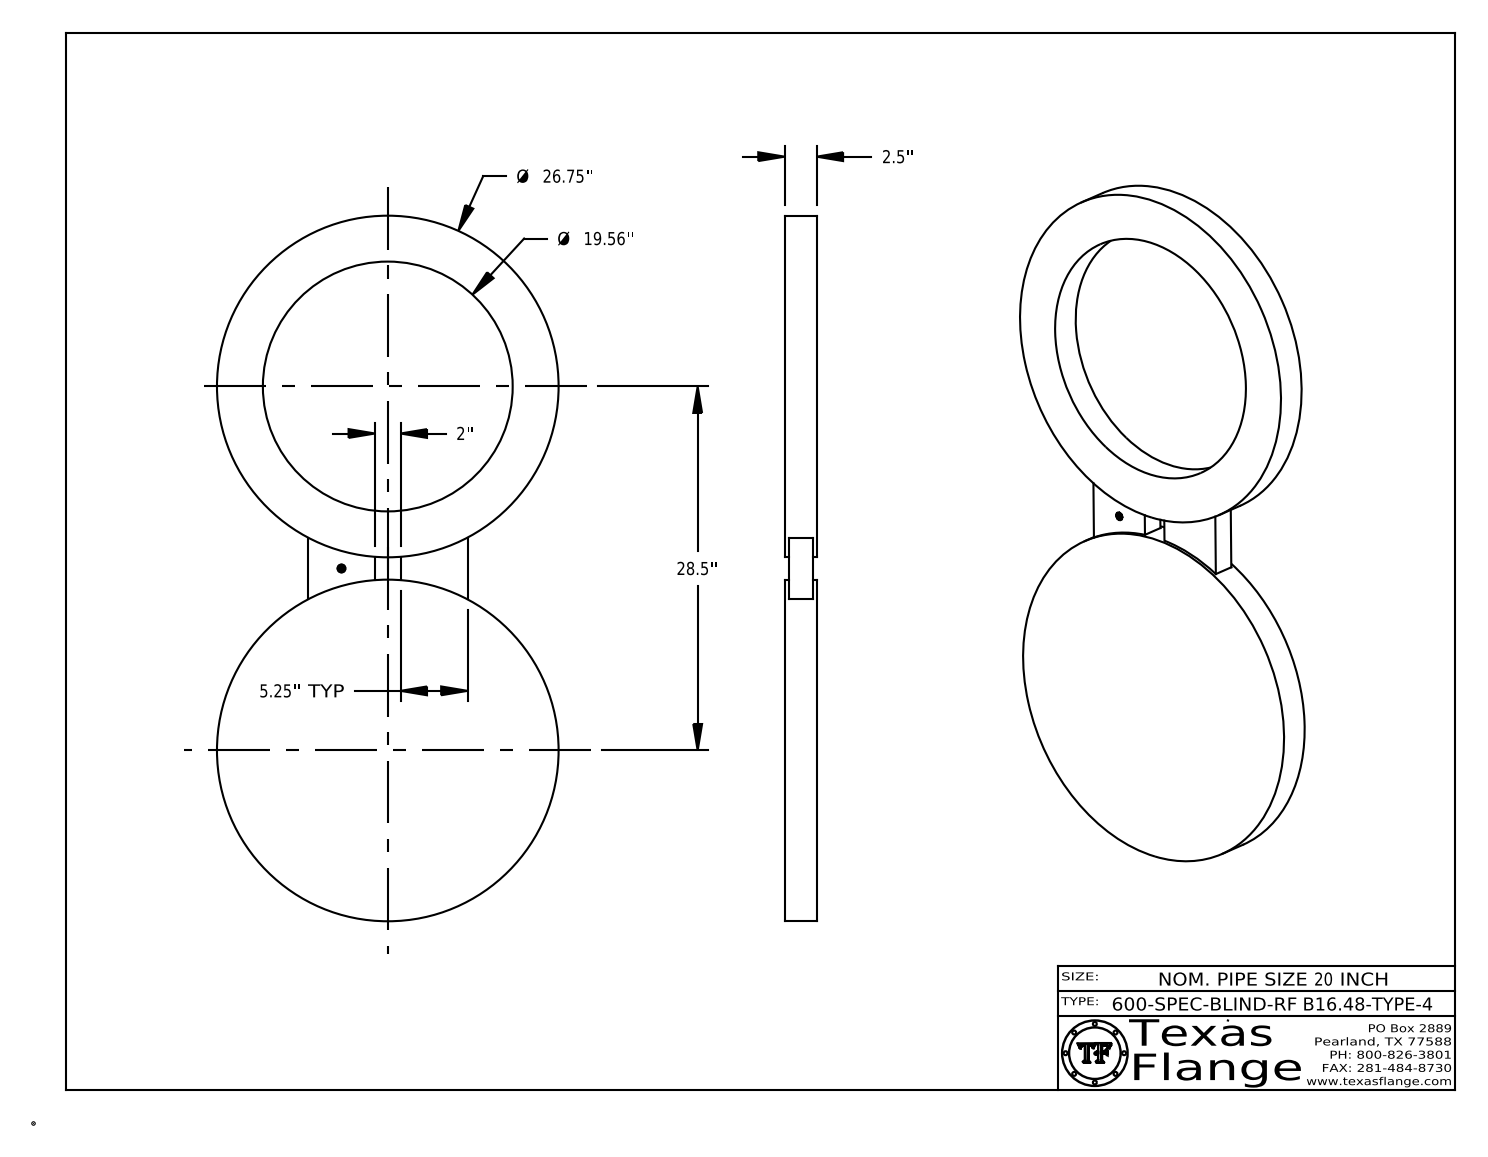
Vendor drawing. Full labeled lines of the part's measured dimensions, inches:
Part name (STEP PRODUCT): 20-600-SPEC-BLIND-RF-B16.48-TYPE-4
STEP written by: CATIA V5 STEP AP214 (AUTOMOTIVE_DESIGN)
Units: inches
Bodies: 1 solid, 403 faces (377 planar, 26 cylindrical, 0 other)
Overall size (bounding box): 55.25 × 26.75 × 2.5
Volume: 2 117 in³ · Surface area: 2 267 in²
Round holes (diameter × count): ⌀0.625 ×1, ⌀19.56 ×1
Round bosses / shafts (diameter × count): ⌀0.038 ×8, ⌀26.75 ×2, ⌀0.492 ×1
Main face-to-face distances: 2.5, 0.313, 2.187, 1.875, 12.5, 5.25, 7.25, 2, 2.172, 1.86
Hole centre spacings: 14.704
